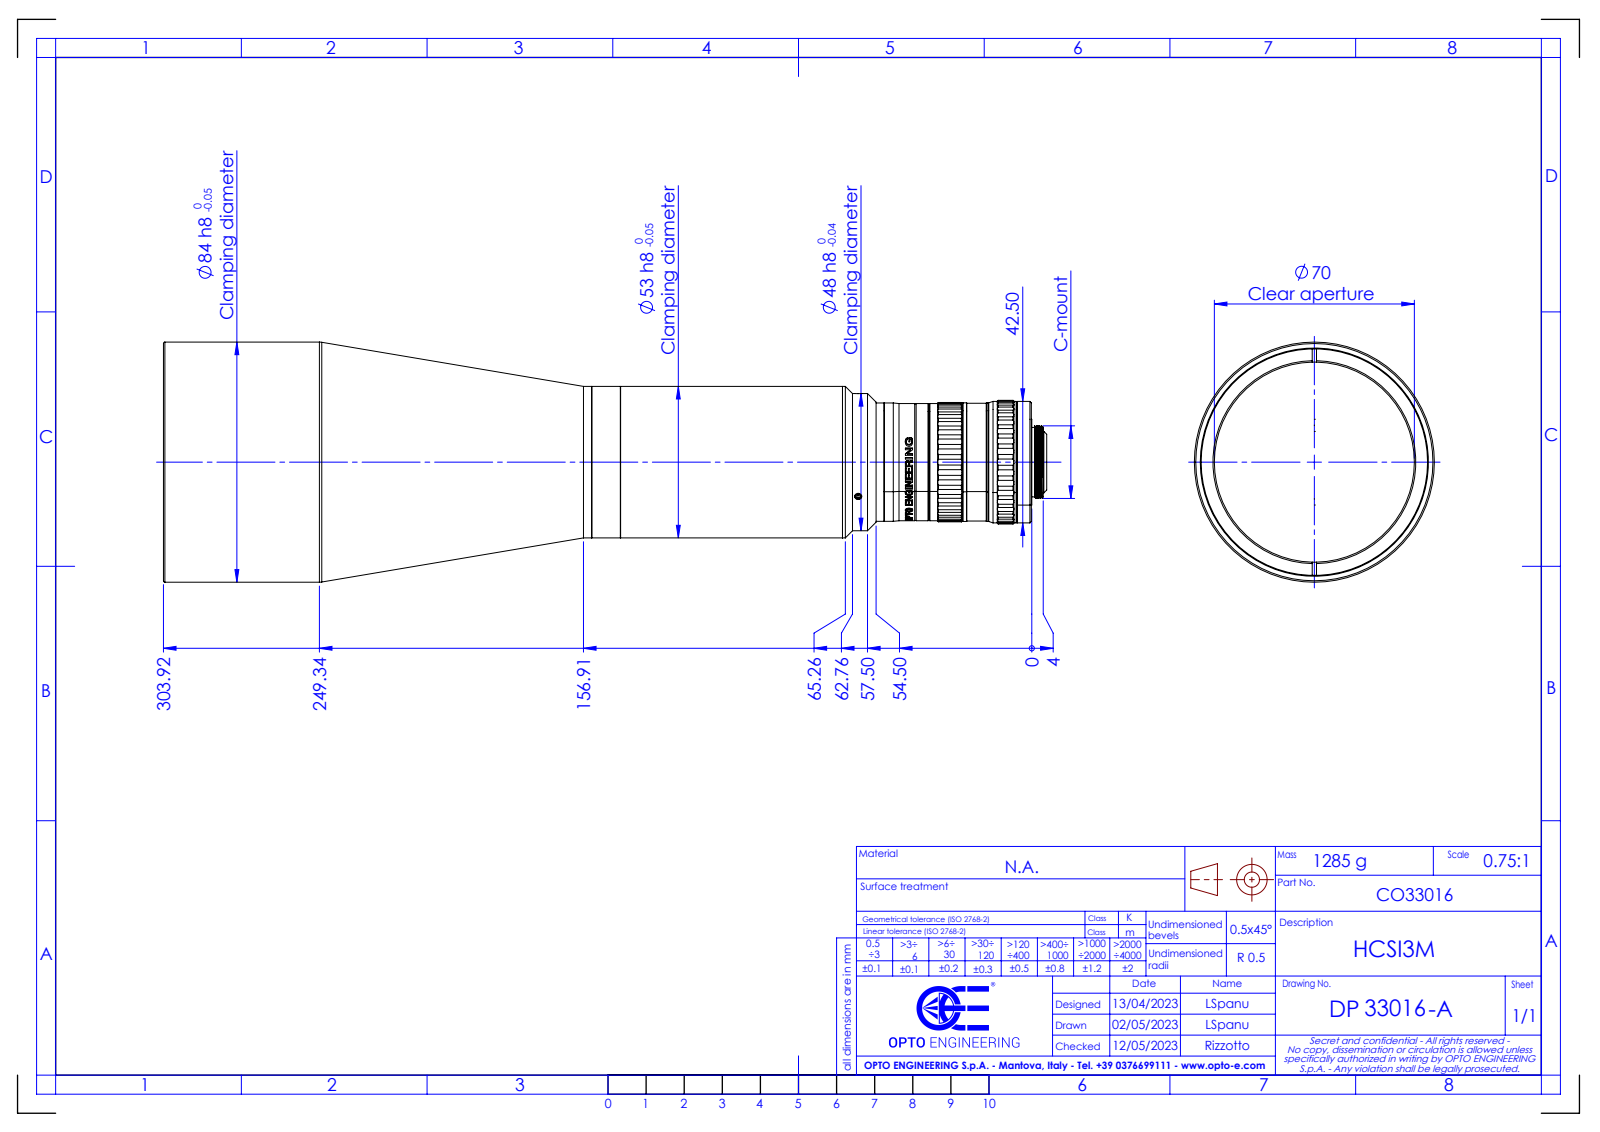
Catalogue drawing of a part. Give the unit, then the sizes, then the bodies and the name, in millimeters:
Units: millimetres
Overall size (bounding box): 309.14 × 84 × 84
Round holes (diameter × count): ⌀1.5 ×3, ⌀2.5 ×3, ⌀2.6 ×3, ⌀13 ×1, ⌀70 ×1, ⌀79.25 ×1
Round bosses / shafts (diameter × count): ⌀84 ×1, ⌀53 ×1, ⌀48 ×1, ⌀42.5 ×1, ⌀41.5 ×1, ⌀41.4 ×1, ⌀41.2 ×1, ⌀41 ×1
Partial cylindrical surfaces — rounded edges, fillets, slot ends (radius × count): R2 ×72, R2.25 ×2, R20.45 ×1, R20.55 ×1, R20.9 ×1, R21.65 ×1
Main face-to-face distances: 2.75, 303.25, 300.5, 159.5, 156.75, 143.75, 0.51, 3.26, 160.01, 303.76
Hole centre spacings: 17.5, 30.3, 17.49, 30.31
Bodies: 0 solids, 712 faces (126 planar, 382 cylindrical, 204 other)
Part name (STEP PRODUCT): DP33016-A_HCSI3M
STEP written by: SolidWorks 2021 (CONFIG_CONTROL_DESIGN)
